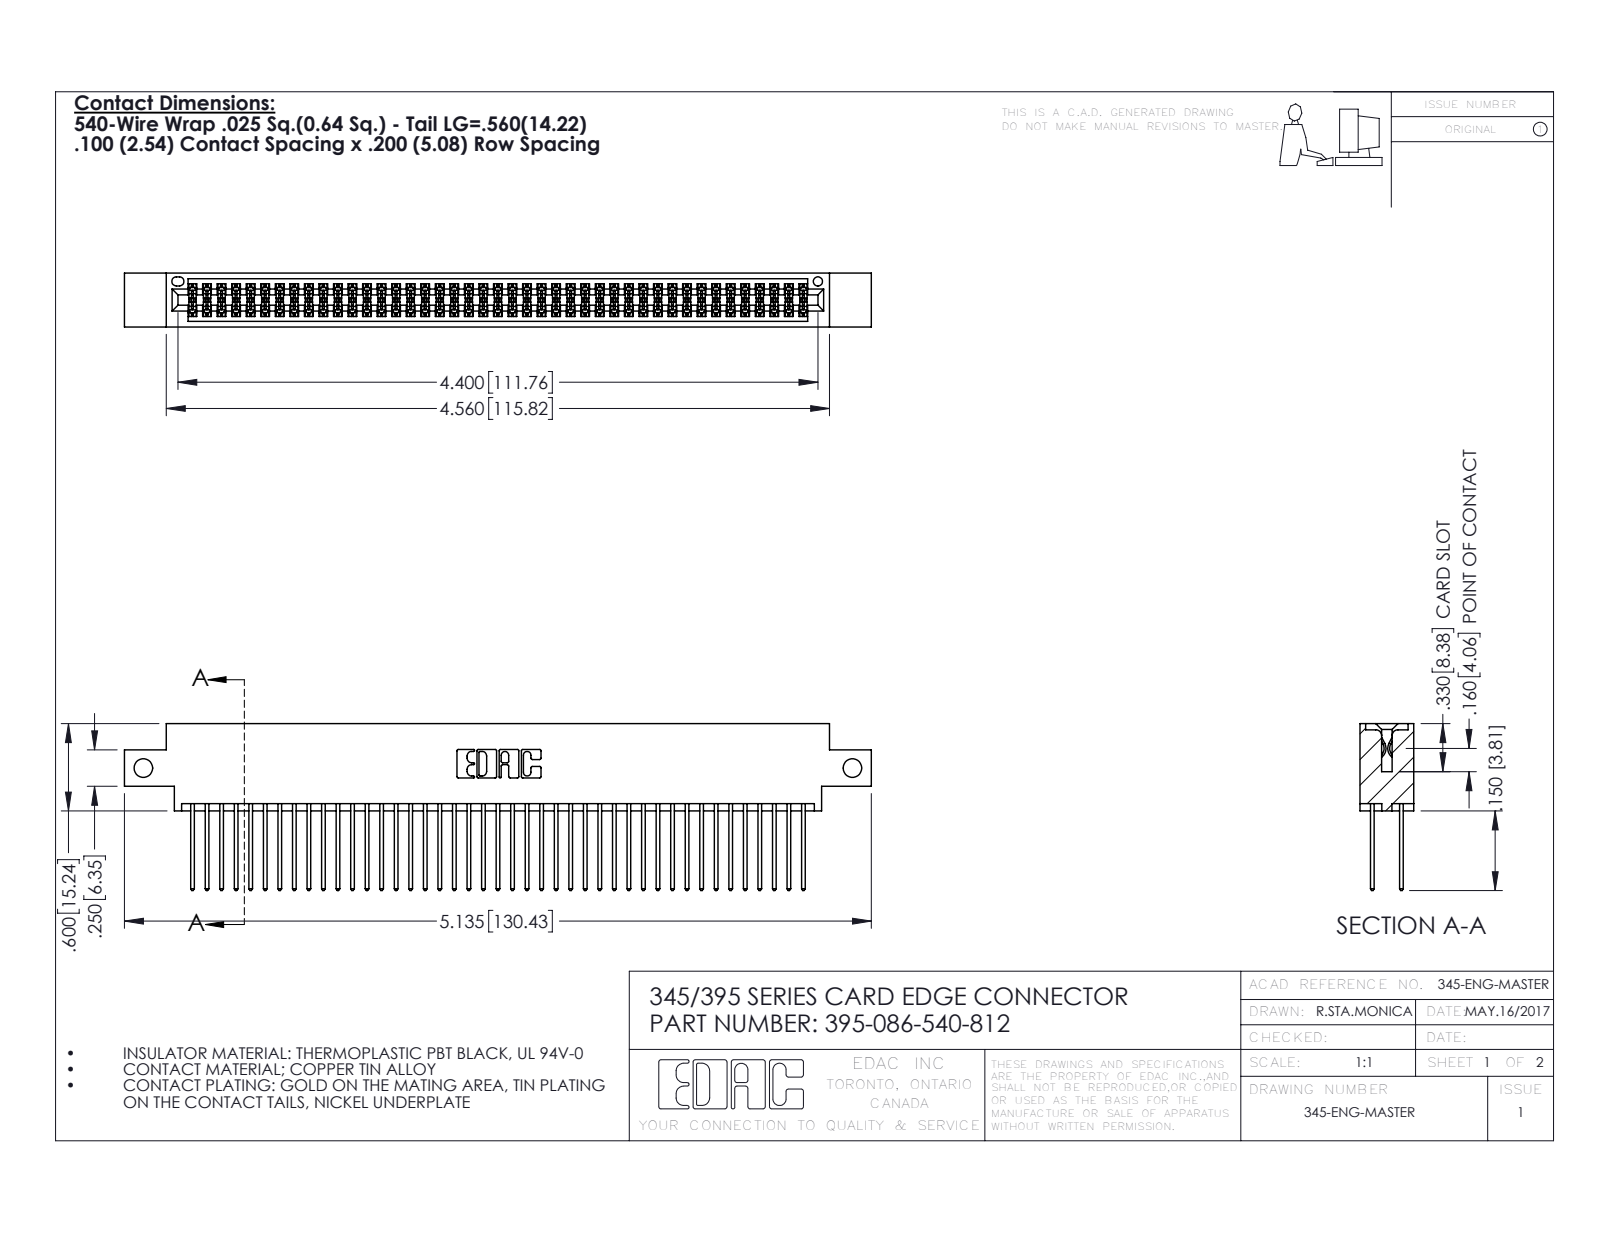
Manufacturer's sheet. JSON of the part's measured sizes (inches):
{"part_name": "345-292-001_345-293-140; 395-086-540-812; 345 Part_0.170 Offset - Side Mount", "step_written_by": "SolidWorks 2016 (CONFIG_CONTROL_DESIGN)", "units": "inches", "bodies": {"solids": 87, "faces": 4430, "planar": 2922, "cylindrical": 1508, "other": 0}, "overall_size": [5.135, 1.147, 0.37], "volume_in3": 0.781, "surface_area_in2": 31.72, "round_holes": [[0.128, 2], [0.064, 1]], "partial_cylinders_radius": [[0.006, 129], [0.01, 86], [0.01, 22], [0.007, 6], [0.031, 6], [0.026, 3], [0.014, 2], [0.019, 2]], "face_to_face_distances": [0.072, 0.298, 0.2, 0.098, 0.272, 0.025, 0.37, 0.225, 0.175, 0.149], "hole_center_spacings": [4.875]}
